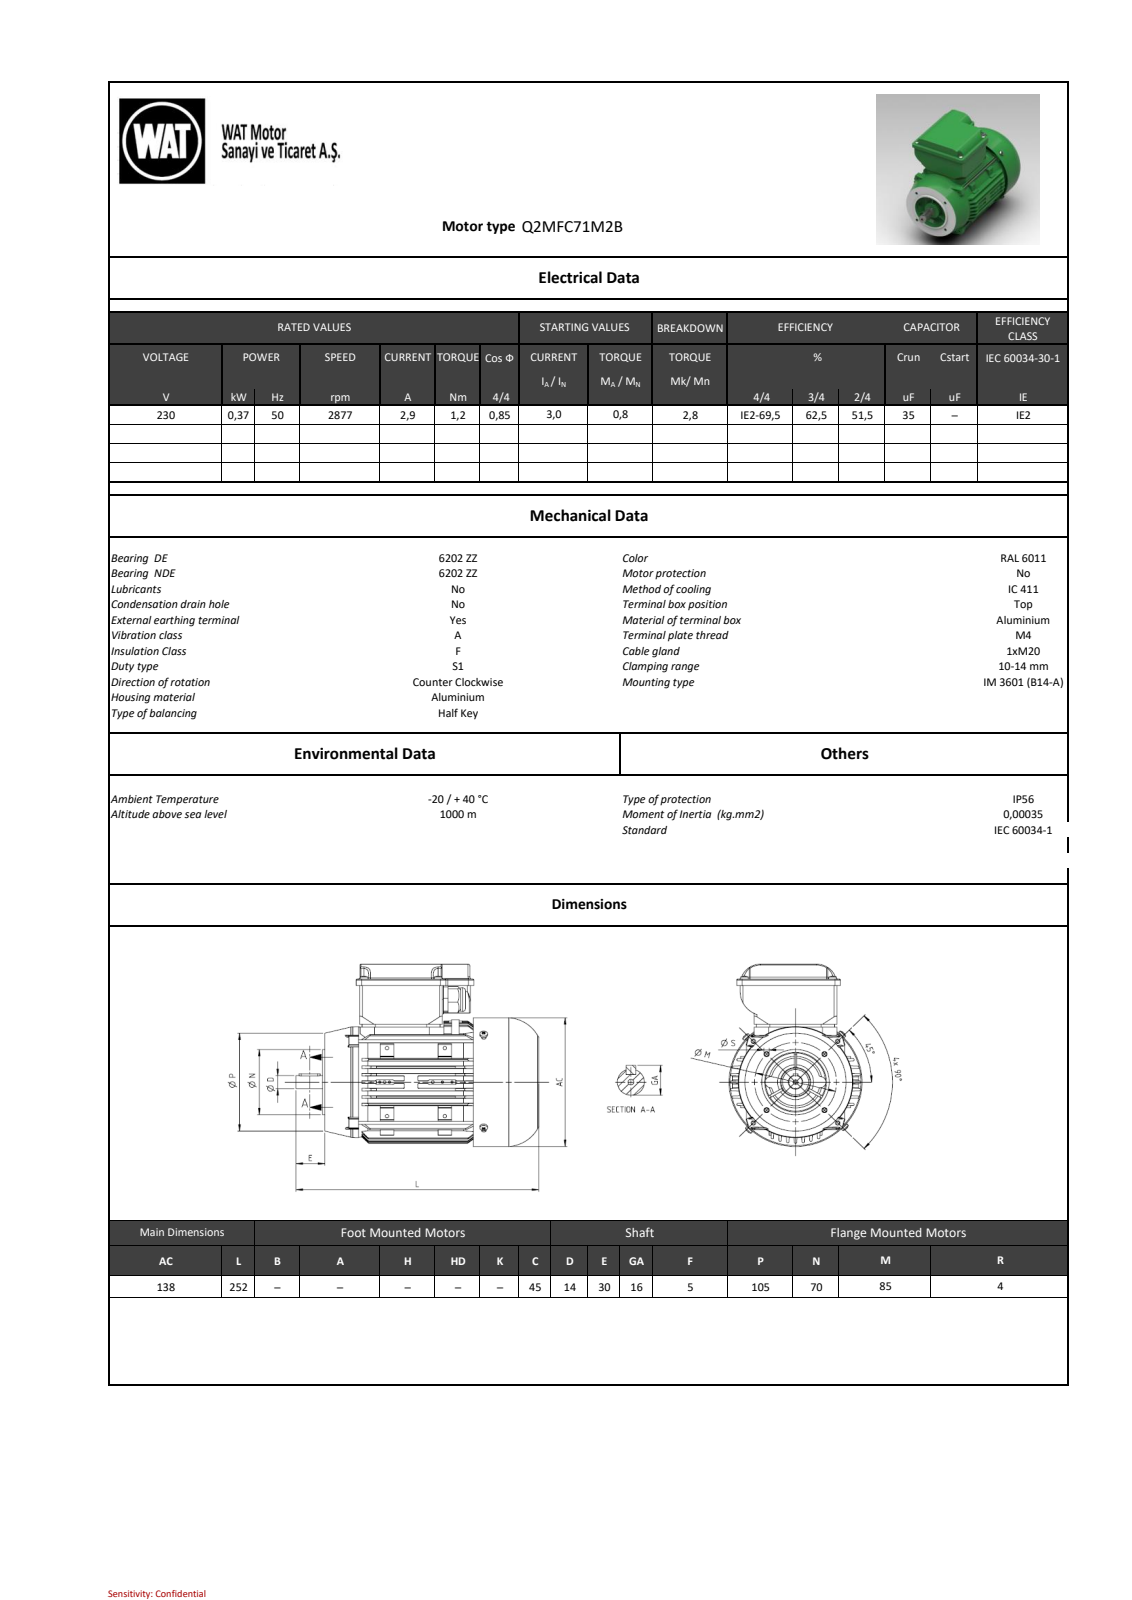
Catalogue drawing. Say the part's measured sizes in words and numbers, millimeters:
The part is named "BY6434017xx_004-TK_QM63-80; BY6424130xx_004-TKK_QM63-80; BY6432003xx_006-MOTOR_KAPAGI_QS71_FC_ISLEME; 641304741_AZ-KAMA PARALEL A 5x5x22 St50 DIN6885 (+7 more)". Its 3-D file was written by "SIEMENS PLM Software NX2206.8101 (AUTOMOTIVE_DESIGN)". It is 24 solids with 2642 faces: 1276 planar, 713 cylindrical and 653 other. Overall it measures 252 by 195.5 by 138 millimeters. Its volume is 695 711 cubic millimeters and its surface area 465 290 square millimeters. Round holes: 9 of diameter 3.3, 8 of diameter 3.65, 8 of diameter 4.5, 7 of diameter 3, 6 of diameter 2.5, 4 of diameter 4.65, 4 of diameter 4.8, 3 of diameter 3.7, 2 of diameter 4.6, 1 of diameter 5, 1 of diameter 6, 1 of diameter 8. Round bosses or shafts: 8 of diameter 8, 8 of diameter 4, 8 of diameter 3, 4 of diameter 12, 4 of diameter 3.3, 1 of diameter 138, 1 of diameter 136, 1 of diameter 70. Partial cylindrical surfaces (rounded edges, fillets, slot ends): 121 of radius 1, 55 of radius 2, 36 of radius 1.2, 35 of radius 0.5, 16 of radius 3.25, 14 of radius 2.5, 13 of radius 5.5, 12 of radius 0.3. The main face-to-face distances are 3, 4, 182.5, 185.5, 146.5, 154.5, 36, 1, 35, 64.5. The hole center spacings are 55, 36.59, 60, 37.26, 61.87, 66.91, 68.11, 73.
